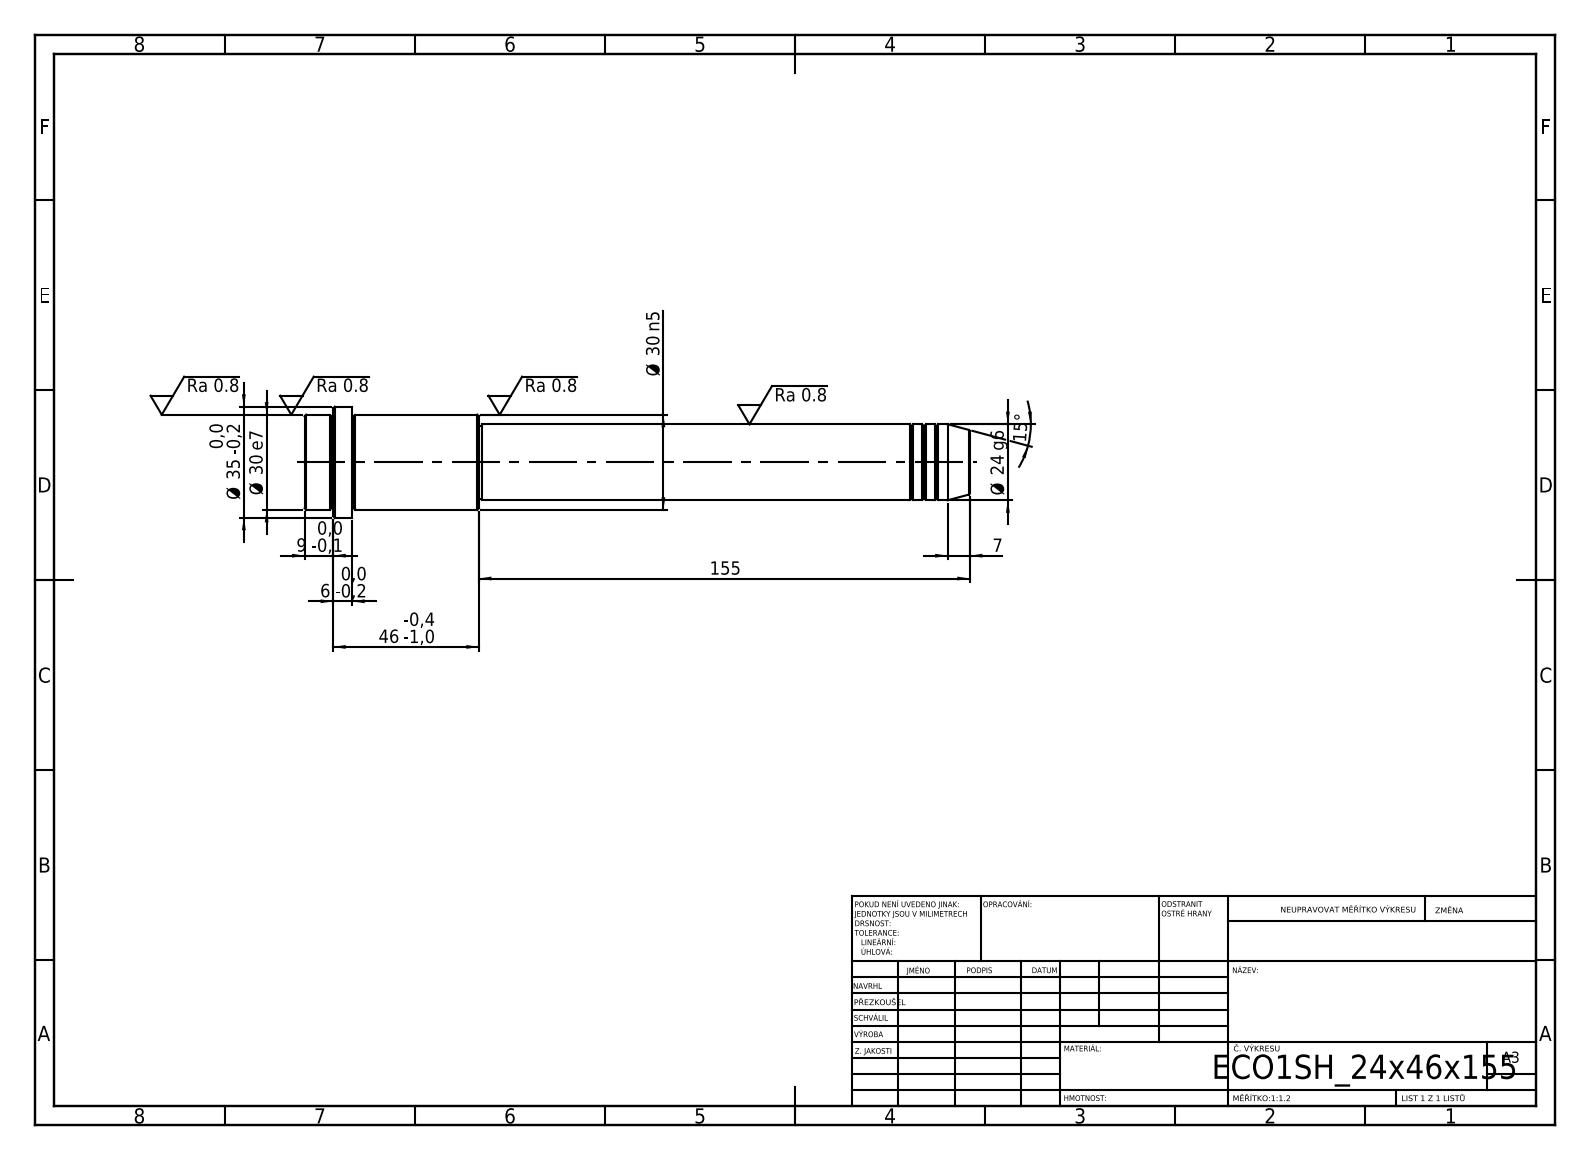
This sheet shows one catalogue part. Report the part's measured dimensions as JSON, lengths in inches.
{"step_written_by": "SolidWorks 2019 (CONFIG_CONTROL_DESIGN)", "units": "inches", "bodies": {"solids": 1, "faces": 52, "planar": 6, "cylindrical": 16, "other": 30}, "overall_size": [8.268, 1.378, 1.378], "volume_in3": 6.702, "surface_area_in2": 29.34, "round_bosses_or_shafts": [[1.378, 1], [1.181, 1], [0.945, 1], [0.906, 1]], "face_to_face_distances": [8.268, 7.677, 0.591, 6.102, 1.575, 2.165, 7.913, 1.811, 0.236, 0.354]}
